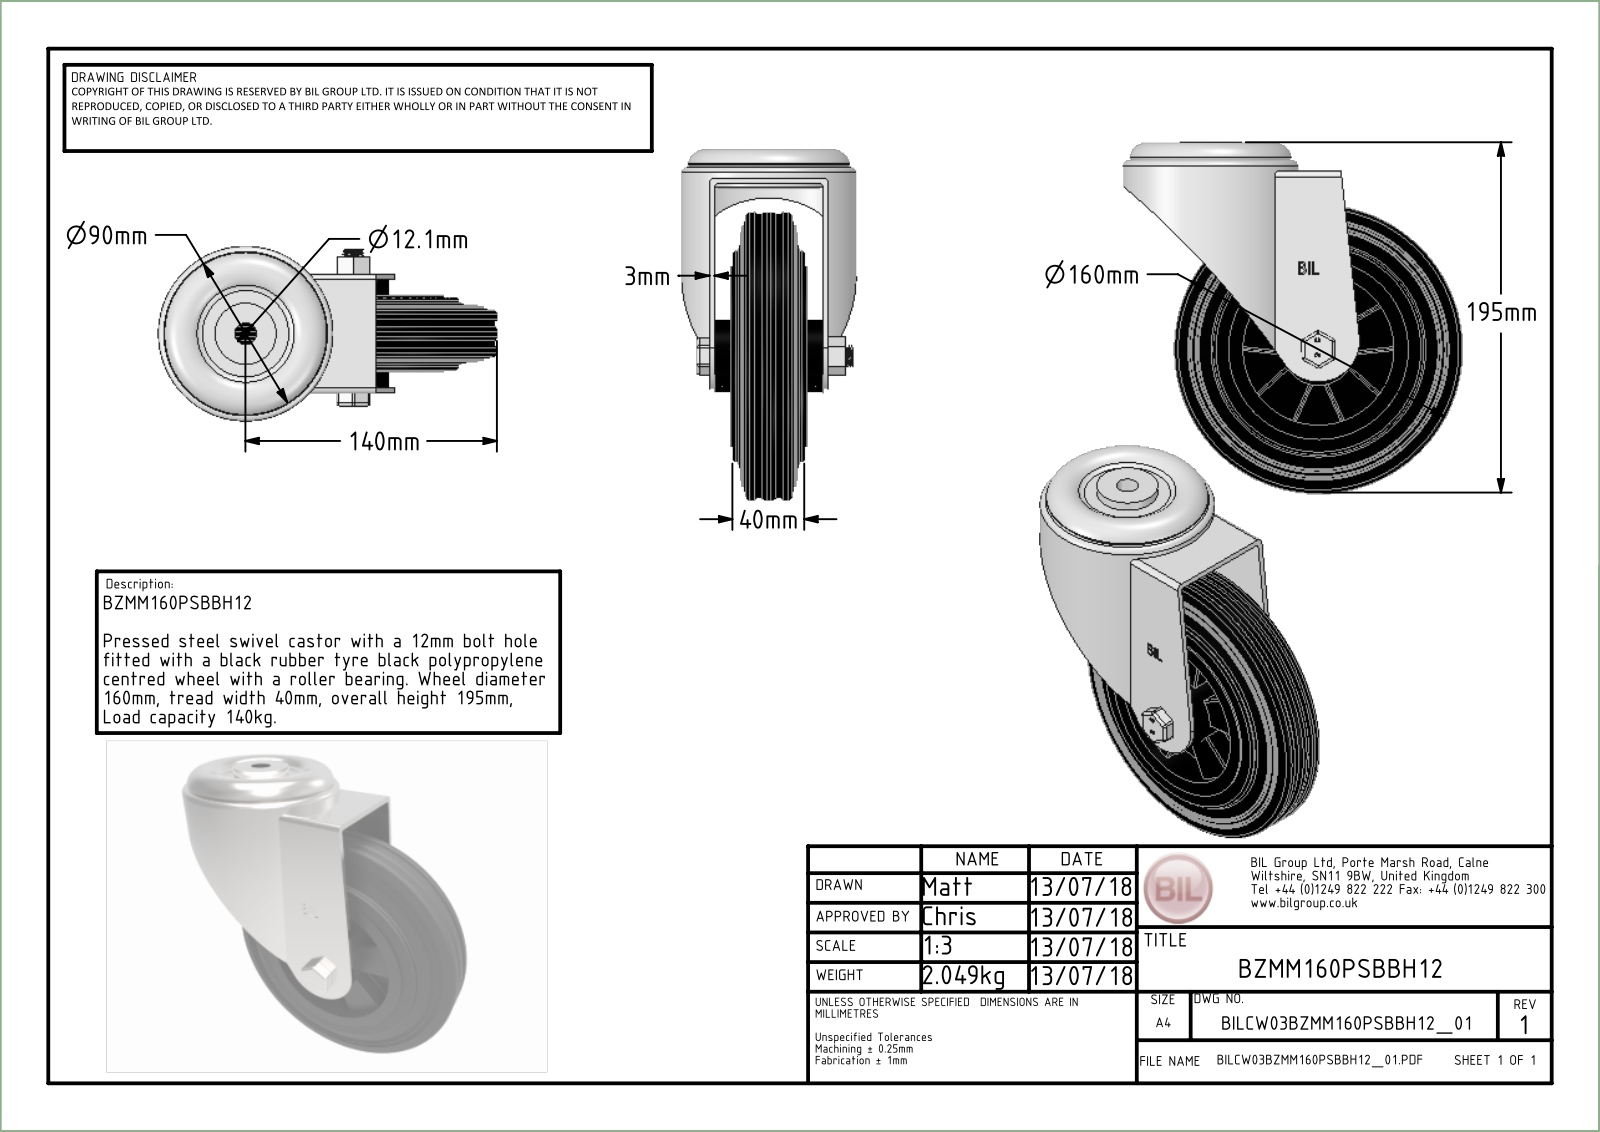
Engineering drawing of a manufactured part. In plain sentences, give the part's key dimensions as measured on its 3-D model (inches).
The part is named "BZMM160PSBBH12 v3; BZMM150ASBH12 v1; ZINC PLATED, PRESSED STEEL FORKS; ZINC PLATED, PRESSED STEEL HEAD (+6 more)". Its 3-D file was written by "Autodesk Translation Framework v13.20.0.188 (AP242_MANAGED_MODEL_BASED_3D_ENGINEERING_MIM_LF)". It is 63 solids with 724 faces: 204 planar, 152 cylindrical and 368 other. Overall it measures 7.677 by 7.48 by 3.937 inches. Its volume is 45.85 cubic inches and its surface area 374.4 square inches. Round holes: 2 of diameter 3.701, 1 of diameter 0.472, 1 of diameter 0.48, 1 of diameter 0.492, 1 of diameter 0.551, 1 of diameter 0.787, 1 of diameter 1.339, 1 of diameter 1.378, 1 of diameter 1.535, 1 of diameter 2.283, 1 of diameter 2.835, 1 of diameter 3.346. Round bosses or shafts: 8 of diameter 0.295, 1 of diameter 6.236, 1 of diameter 3.976, 1 of diameter 3.937, 1 of diameter 2.48, 1 of diameter 1.575, 1 of diameter 1.374, 1 of diameter 1.339. Partial cylindrical surfaces (rounded edges, fillets, slot ends): 18 of radius 0.02, 12 of radius 0.039, 4 of radius 0.059, 2 of radius 0.118, 1 of radius 0.531, 1 of radius 0.888, 1 of radius 3.071, 1 of radius 19.782. The main face-to-face distances are 0.118, 2.48, 0.453, 2.028, 0.236, 2.362, 0.335, 0.098, 1.388, 0.758.
